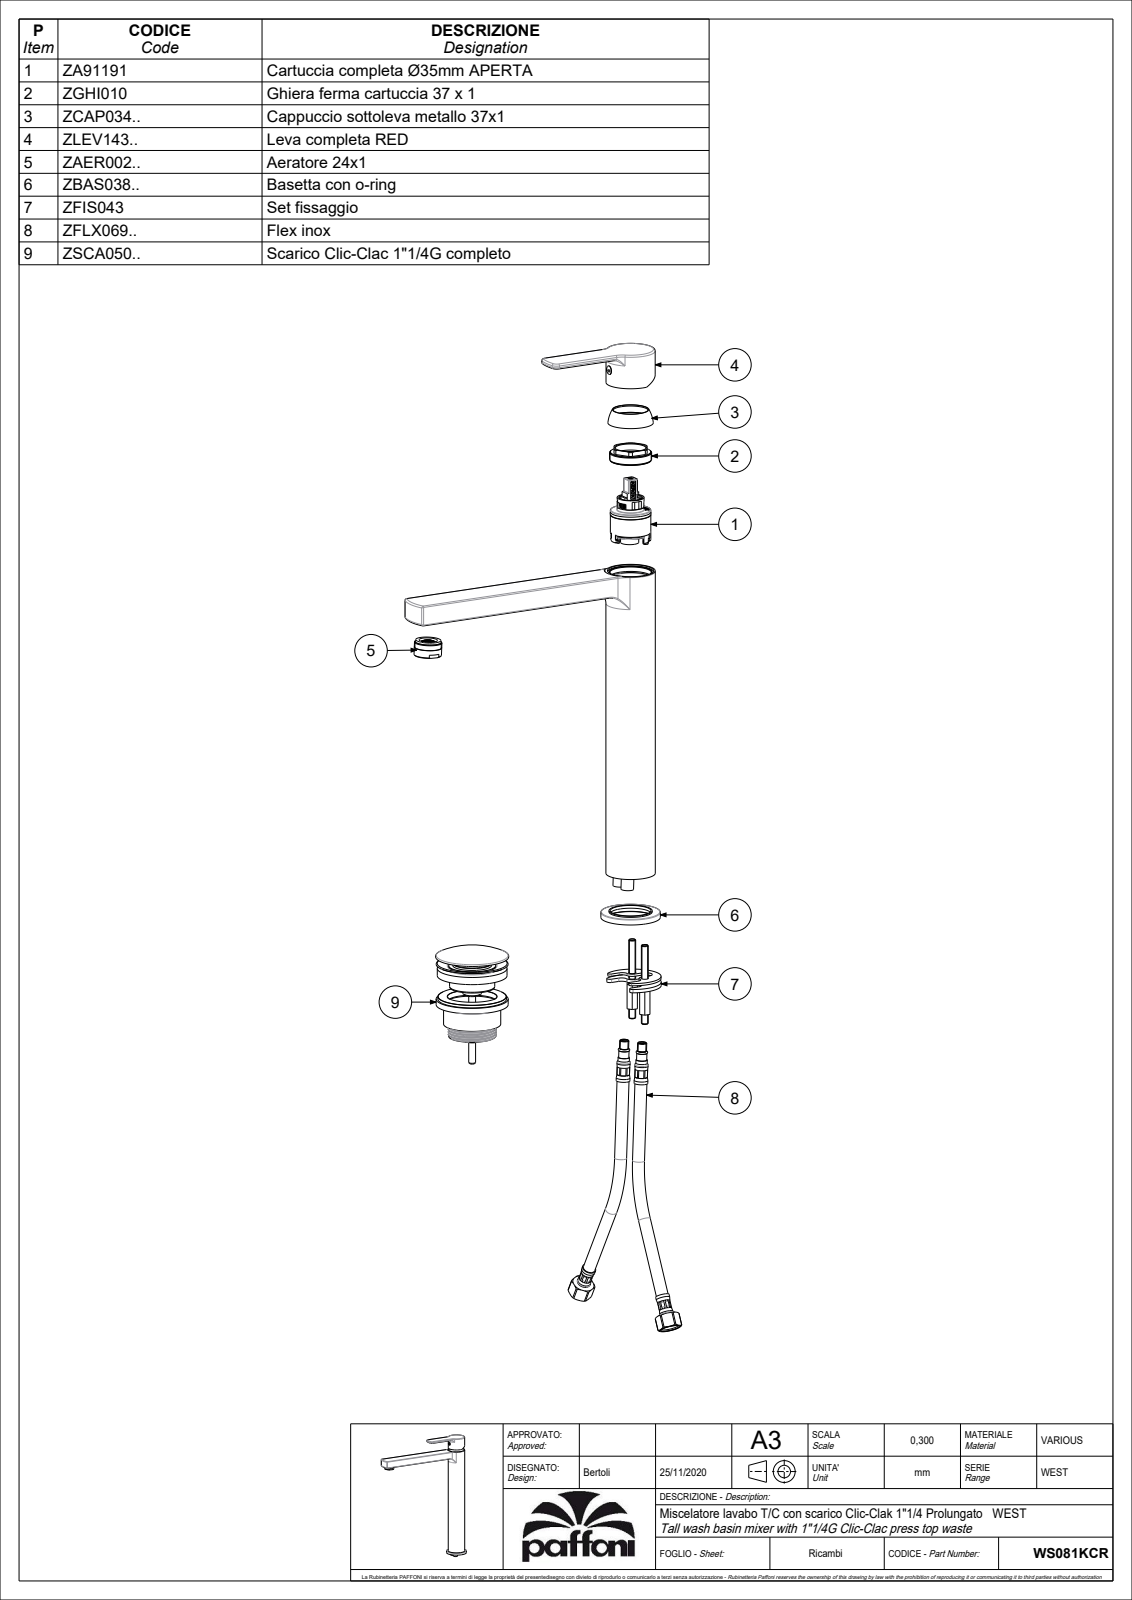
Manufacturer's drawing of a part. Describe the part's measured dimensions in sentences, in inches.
The part is named "WS081CR". Its 3-D file was written by "CREO PARAMETRIC BY PTC INC, 2020044 (CONFIG_CONTROL_DESIGN)". It is 2 solids with 3363 faces: 2396 planar, 537 cylindrical and 430 other. Overall it measures 12.393 by 9.764 by 2.047 inches. Its volume is 15.73 cubic inches and its surface area 262.6 square inches. Round holes: 4 of diameter 0.236, 2 of diameter 0.197, 2 of diameter 0.217, 2 of diameter 0.256, 2 of diameter 0.315, 2 of diameter 0.323, 1 of diameter 0.118, 1 of diameter 0.13, 1 of diameter 0.134, 1 of diameter 0.138, 1 of diameter 0.157, 1 of diameter 0.177. Round bosses or shafts: 4 of diameter 0.315, 2 of diameter 0.189, 2 of diameter 0.157, 1 of diameter 2.047, 1 of diameter 1.701, 1 of diameter 1.693, 1 of diameter 1.677, 1 of diameter 1.488. Partial cylindrical surfaces (rounded edges, fillets, slot ends): 85 of radius 0.02, 24 of radius 0.059, 18 of radius 0.039, 6 of radius 0.067, 5 of radius 0.079, 4 of radius 0.031, 4 of radius 0.228, 3 of radius 0.502. The main face-to-face distances are 0.138, 0.571, 0.709, 0.433, 1.083, 1.22, 1.911, 1.774, 1.341, 1.203. The hole center spacings are 0.551, 0.535, 0.111, 0.339, 0.53, 0.596, 0.791, 0.863.
